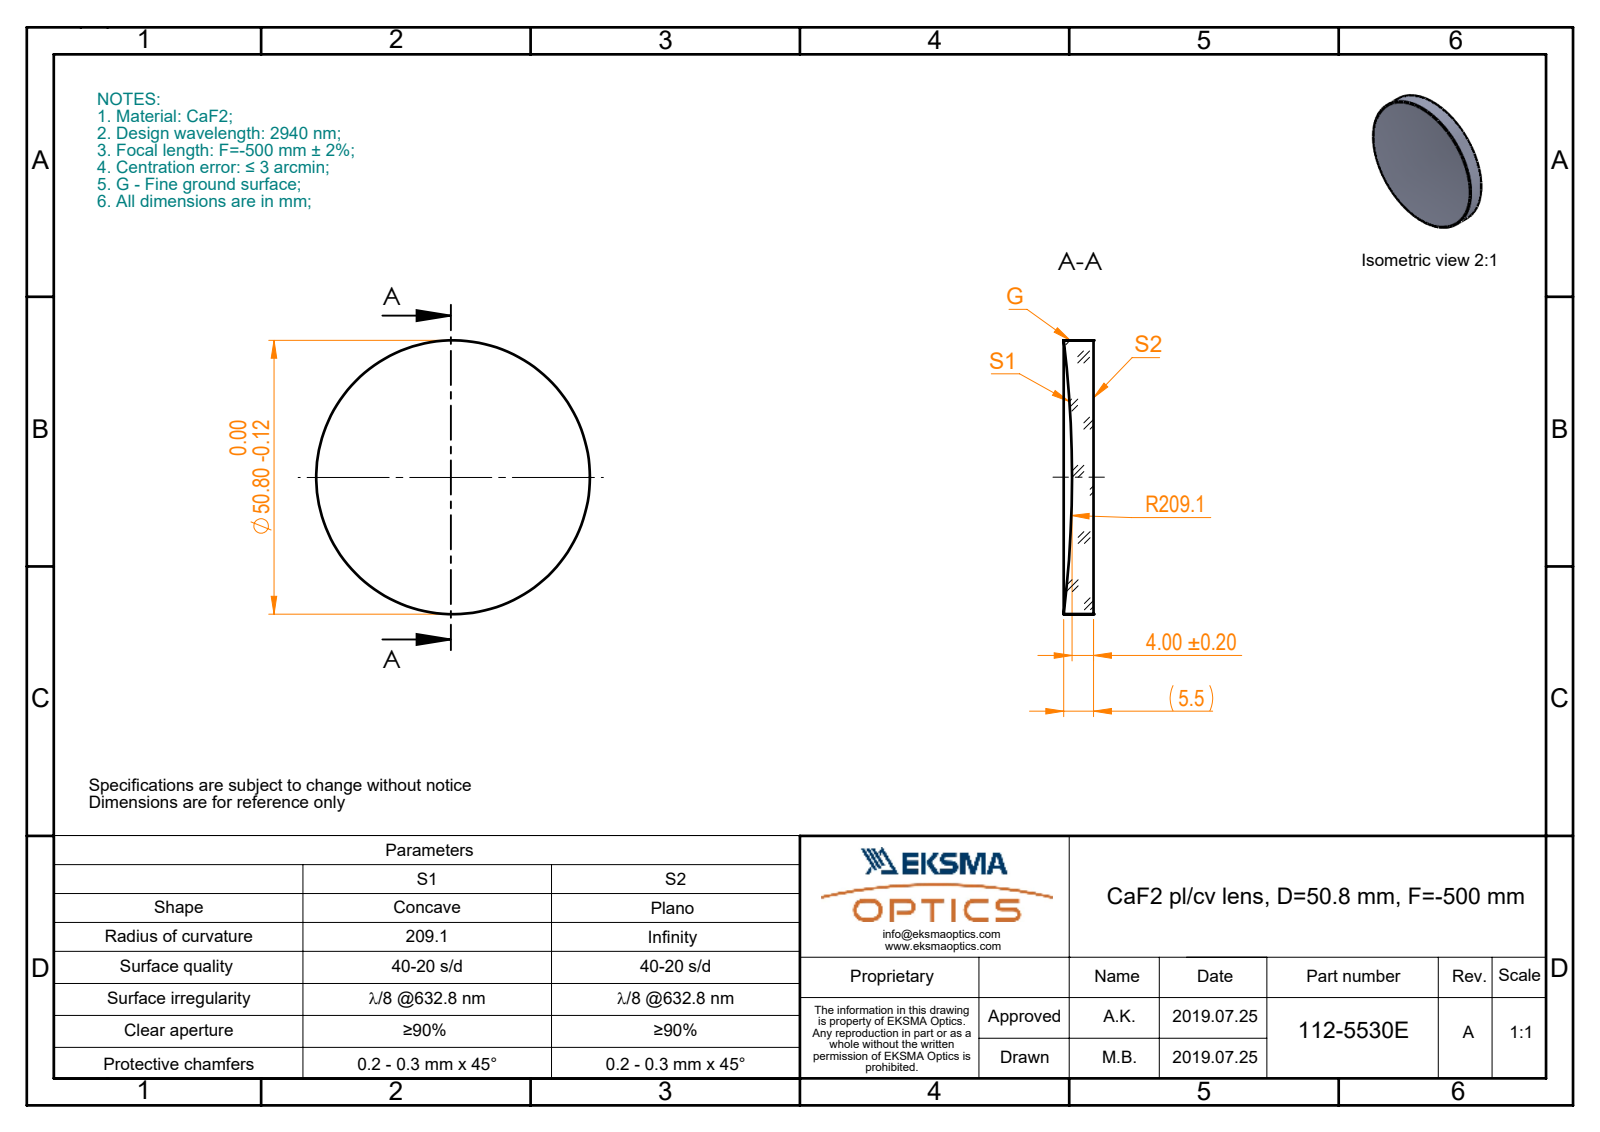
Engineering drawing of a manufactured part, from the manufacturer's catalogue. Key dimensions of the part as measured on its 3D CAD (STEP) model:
Part name (STEP PRODUCT): 112-5530E CaF2 pl-cv 50.8 F-500
STEP written by: SolidWorks 2017 (CONFIG_CONTROL_DESIGN)
Units: millimetres
Bodies: 1 solid, 5 faces (1 planar, 2 cylindrical, 2 other)
Overall size (bounding box): 50.8 × 50.8 × 5.55
Volume: 9 675 mm³ · Surface area: 4 947 mm²
Round bosses / shafts (diameter × count): ⌀50.8 ×1
